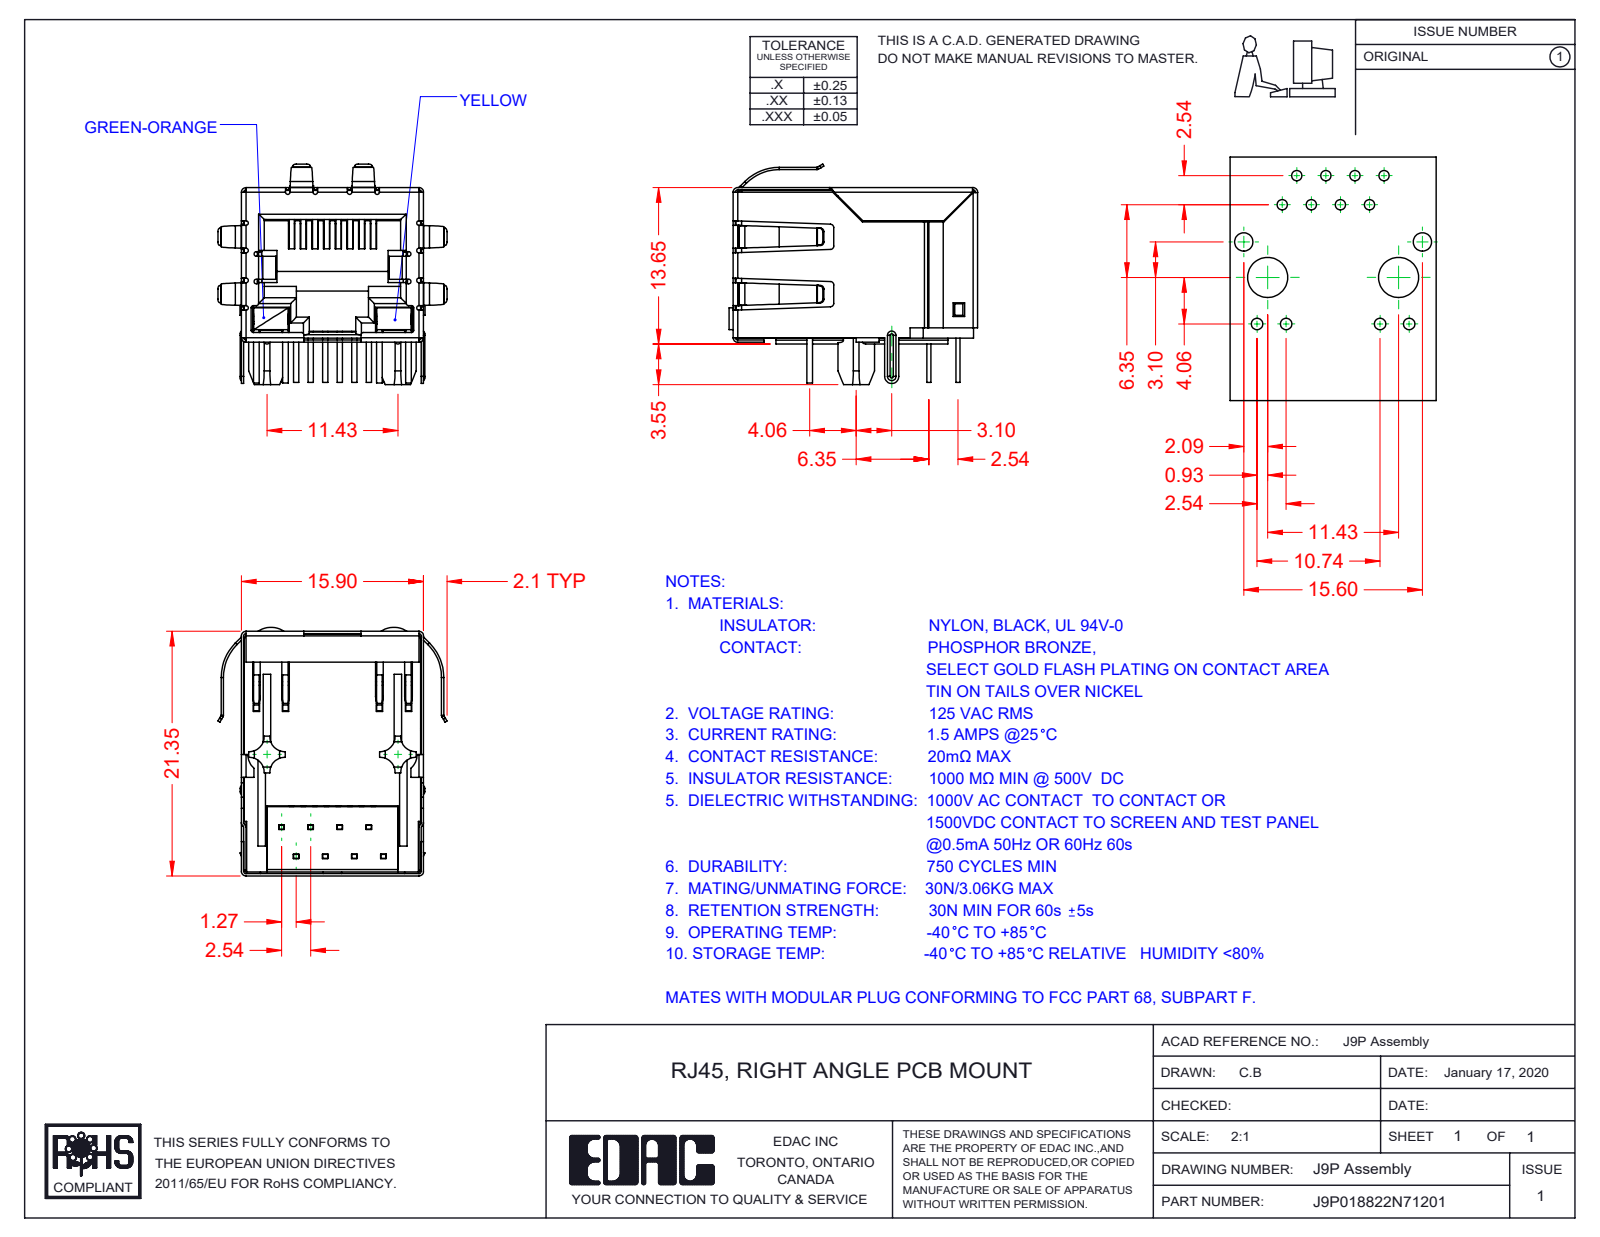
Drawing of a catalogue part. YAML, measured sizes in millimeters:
part_name: "9P-LED Shield; 9P-LED LED LH_7-Green-Orange; 9P-LED Assembly; 9P-LED Contacts (+4 more)"
step_written_by: "SolidWorks 2016 (CONFIG_CONTROL_DESIGN)"
units: millimeters
bodies: {solids: 13, faces: 1474, planar: 1042, cylindrical: 338, other: 94}
overall_size: [21.7, 20, 19.25]
volume: 2687
surface_area: 7515
partial_cylinders:
  - {radius: 0.2, count: 39}
  - {radius: 0.5, count: 22}
  - {radius: 0.3, count: 20}
  - {radius: 0.4, count: 16}
  - {radius: 1.3, count: 8}
  - {radius: 0.23, count: 5}
  - {radius: 0.11, count: 4}
  - {radius: 0.31, count: 4}
face_to_face_distances: [15.45, 15.7, 15.65, 0.35, 0.54, 15.5, 12.36, 0.6, 1.4, 0.59]
